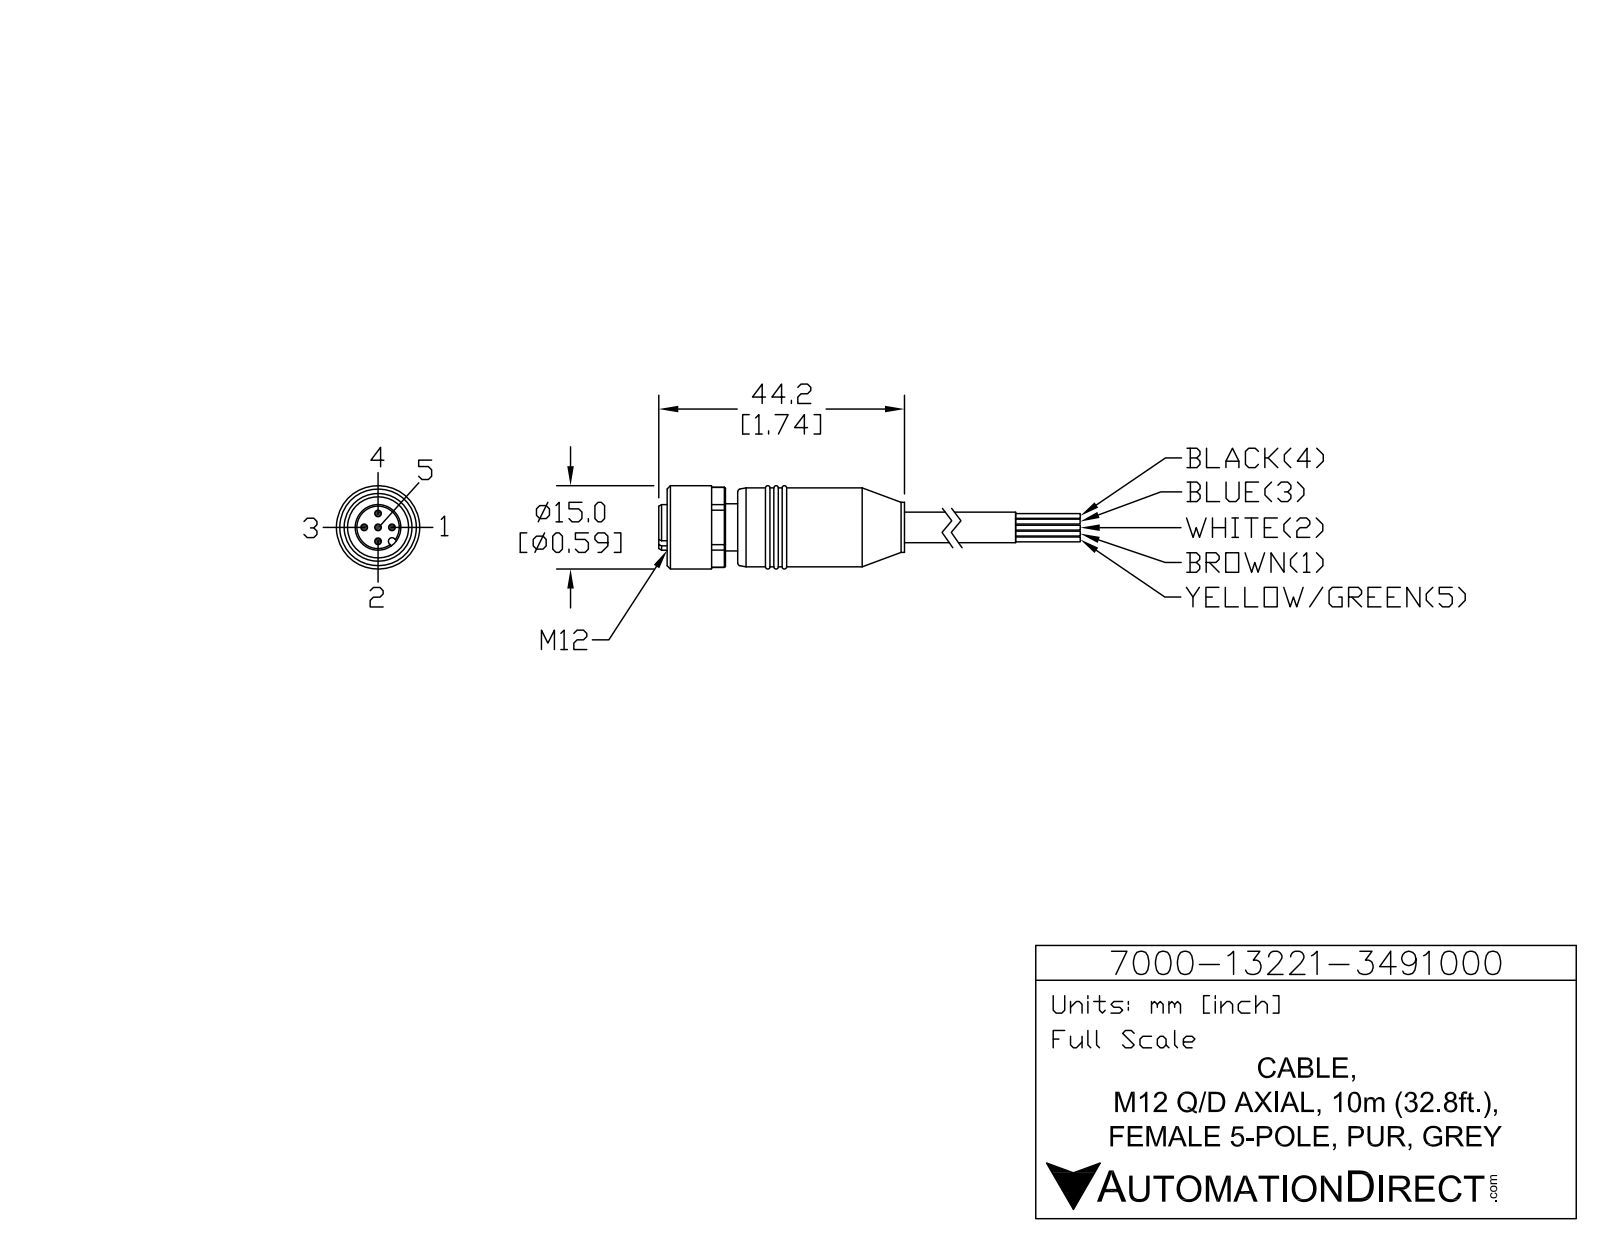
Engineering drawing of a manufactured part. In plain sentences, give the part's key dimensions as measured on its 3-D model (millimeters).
The part is named "7000-13221-3491000". Its 3-D file was written by "SolidWorks 2015 (AUTOMOTIVE_DESIGN)". It is 1 solid with 94 faces: 28 planar, 38 cylindrical and 28 other. Overall it measures 64.2 by 15 by 15 millimeters. Its volume is 6 622 cubic millimeters and its surface area 3 349 square millimeters. Round holes: 5 of diameter 1.2, 1 of diameter 11. Round bosses or shafts: 1 of diameter 15, 1 of diameter 14.2, 1 of diameter 9, 1 of diameter 8.5, 1 of diameter 8.2, 1 of diameter 6.5. Partial cylindrical surfaces (rounded edges, fillets, slot ends): 1 of radius 0.65, 1 of radius 7.2. The main face-to-face distances are 2.2, 13, 3, 5.2, 9, 12, 14.2, 64.2, 55.2, 52.2. The hole center spacings are 2.5, 3.54, 5.
